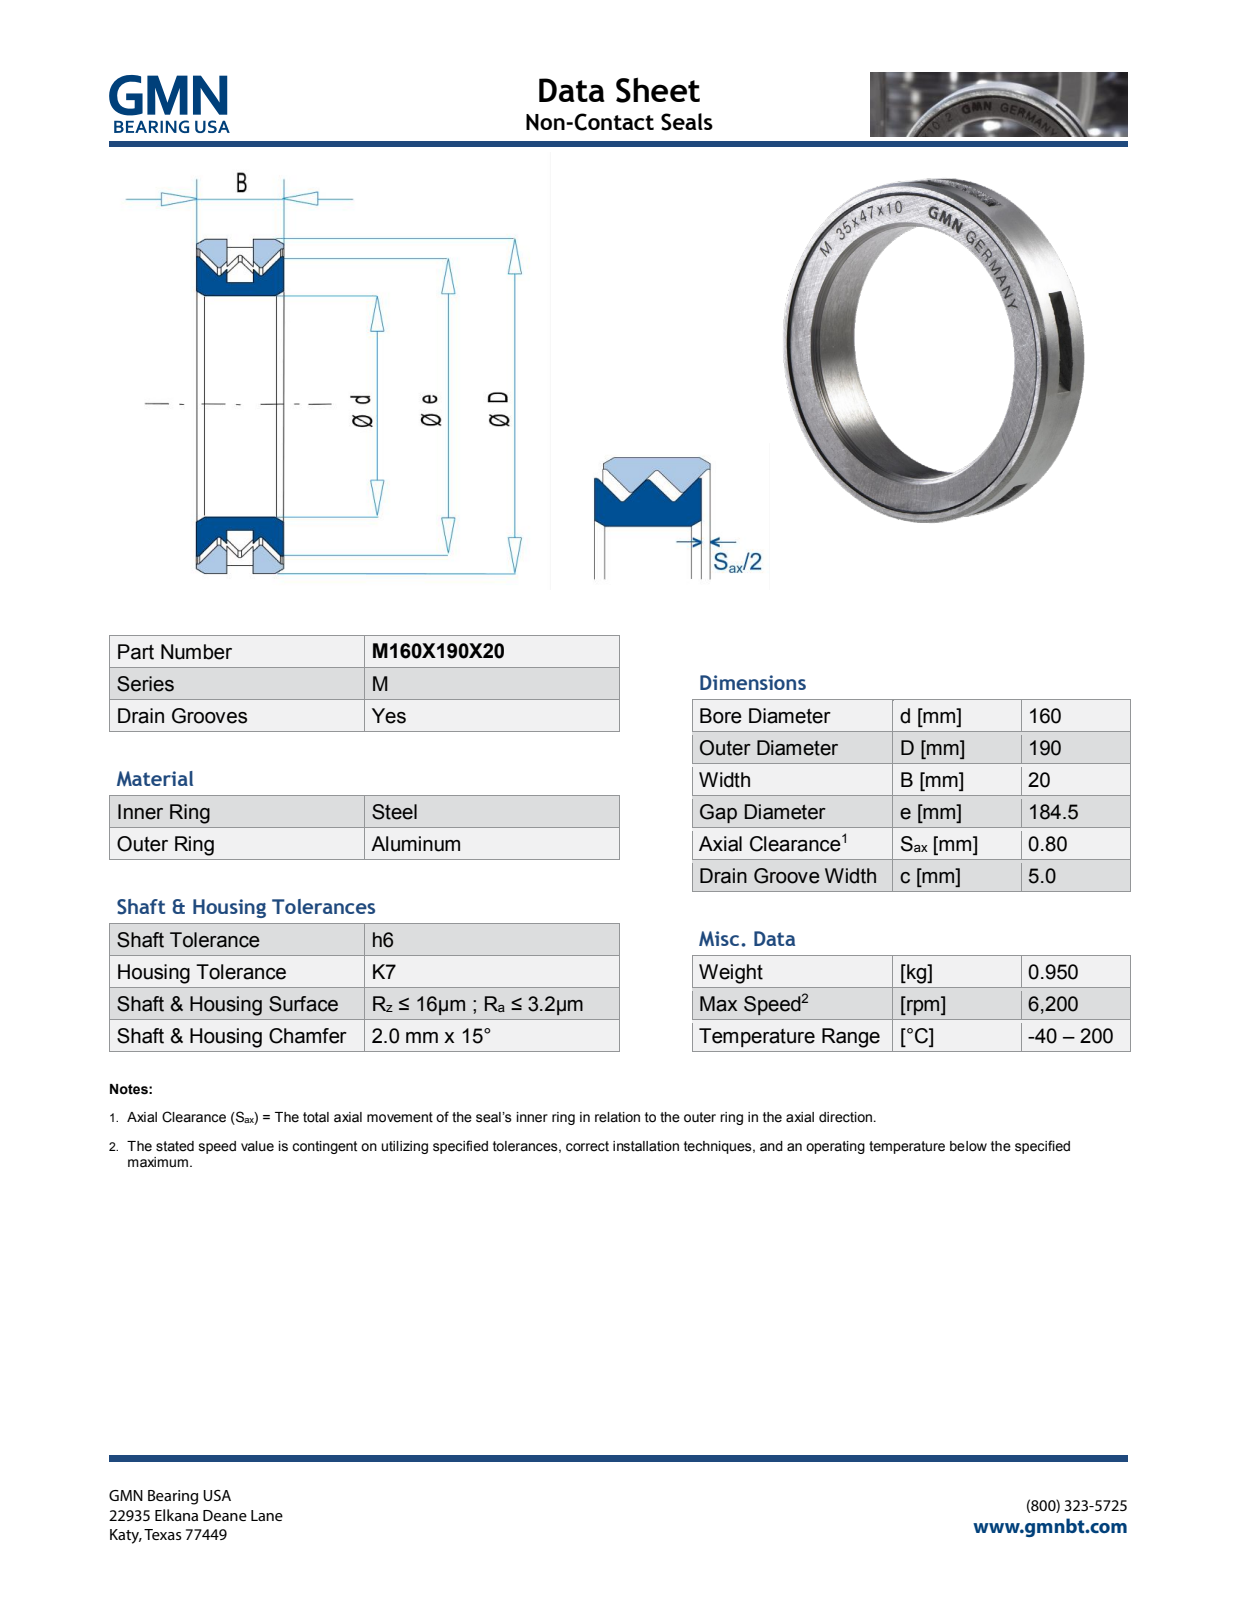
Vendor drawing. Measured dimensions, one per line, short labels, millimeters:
name: M160X190X20_PRT
written by: PRO/ENGINEER BY PARAMETRIC TECHNOLOGY CORPORATION, 2013150 (AUTOMOTIVE_DESIGN)
unit: mm
bodies: 2 solids, 808 faces (669 planar, 45 cylindrical, 94 other)
size: 190 × 190 × 20.08
volume: 151 665 mm³; area: 68 392 mm²
holes: 1× ⌀160, 1× ⌀185.09
bosses: 1× ⌀190, 1× ⌀184.5
rounds: 11× R10
face distances: 20, 7.5, 12.5, 5, 7.58, 12.58, 20.08, 1.14, 9.1, 7.96
